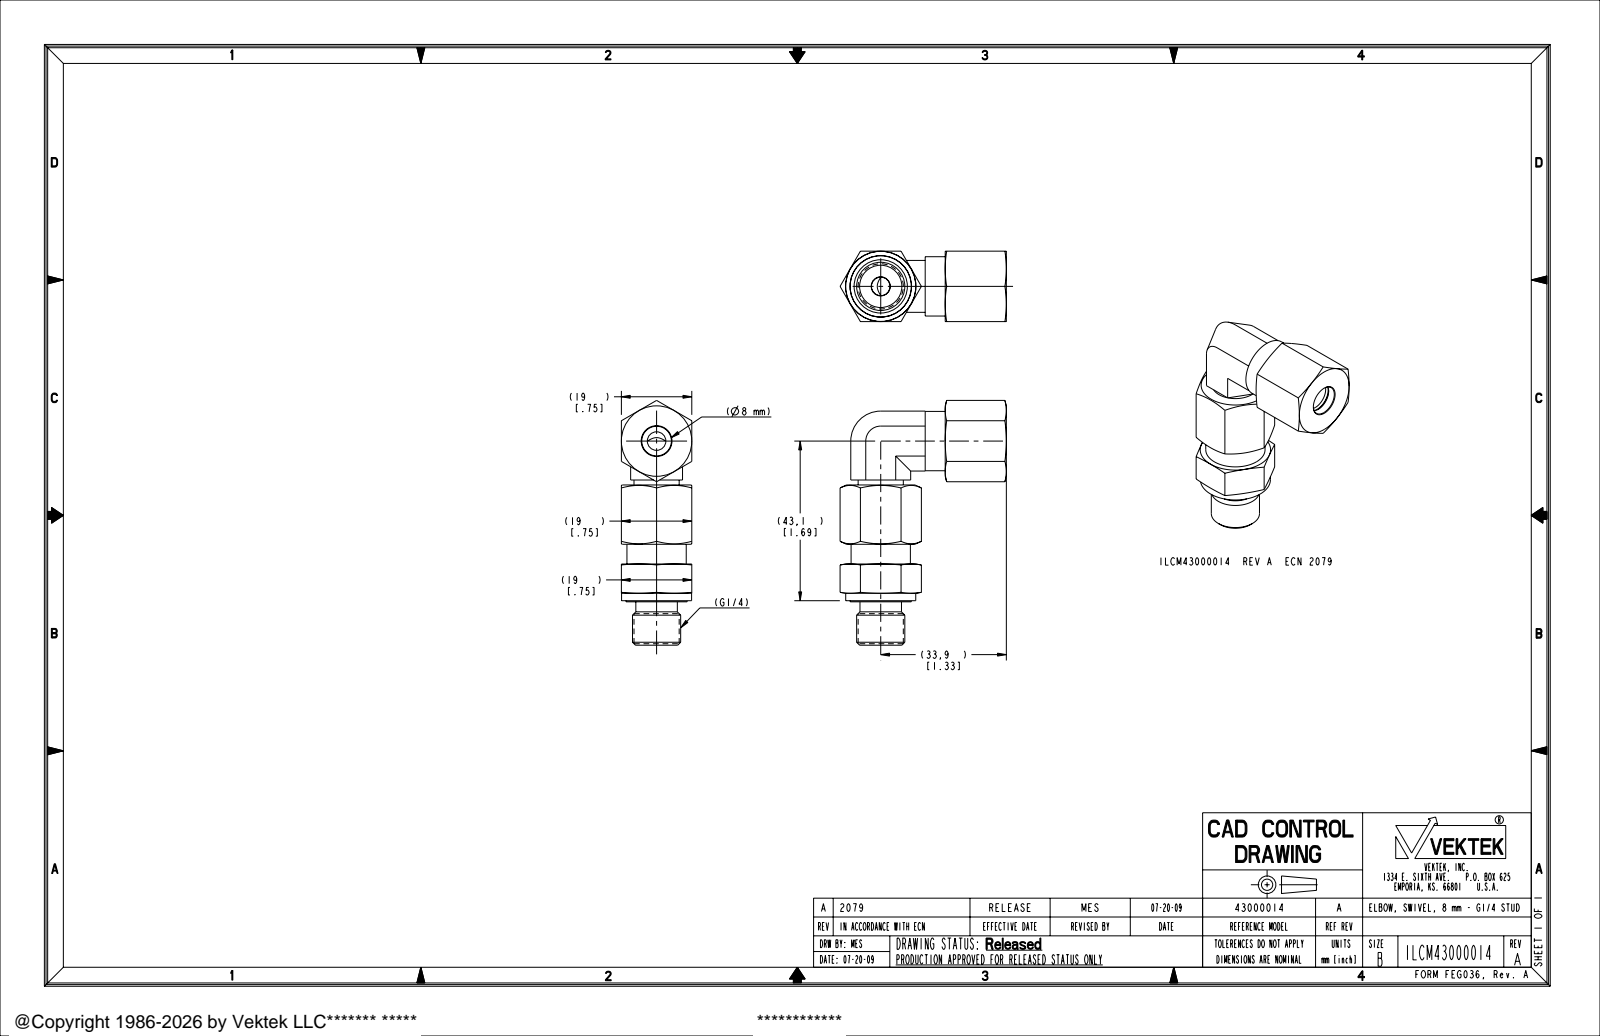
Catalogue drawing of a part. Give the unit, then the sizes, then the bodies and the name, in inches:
Units: inches
Overall size (bounding box): 2.599 × 1.767 × 0.748
Round holes (diameter × count): ⌀0.197 ×2, ⌀0.315 ×2, ⌀0.457 ×1, ⌀0.492 ×1, ⌀0.566 ×1, ⌀0.571 ×1, ⌀0.654 ×1
Round bosses / shafts (diameter × count): ⌀0.63 ×2, ⌀0.744 ×1, ⌀0.65 ×1, ⌀0.512 ×1, ⌀0.48 ×1, ⌀0.441 ×1, ⌀0.433 ×1, ⌀0.398 ×1
Main face-to-face distances: 0.748, 0.65, 0.098, 0.551, 0.472, 0.862, 0.39, 1.281, 0.419, 0.839
Volume: 1.06 in³ · Surface area: 15.37 in²
Bodies: 1 solid, 183 faces (63 planar, 46 cylindrical, 74 other)
Part name (STEP PRODUCT): ILCM43000014
STEP written by: PRO/ENGINEER BY PARAMETRIC TECHNOLOGY CORPORATION, 2007460 (AUTOMOTIVE_DESIGN_CC2)
